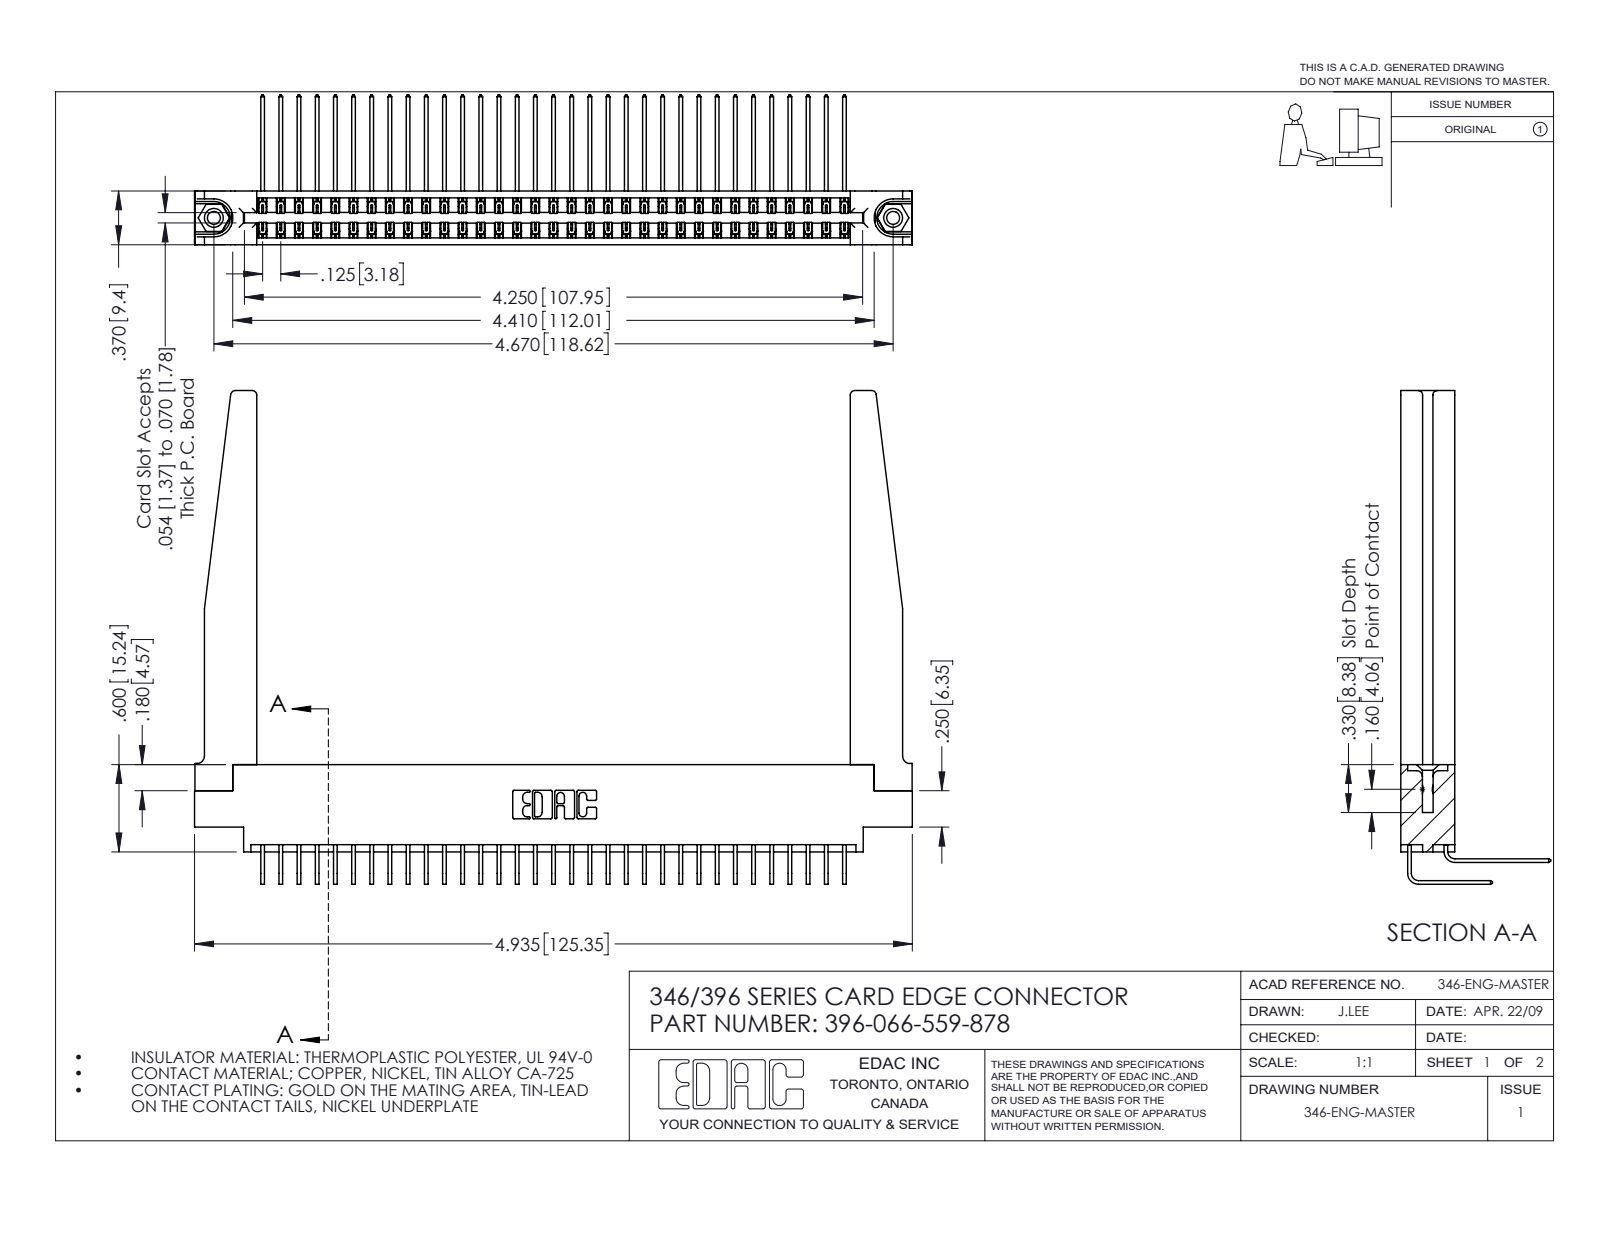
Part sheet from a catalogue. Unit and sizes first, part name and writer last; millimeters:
Units: millimetres
Overall size (bounding box): 125.3 × 86.2 × 26.2
Round holes (diameter × count): ⌀2.3 ×2, ⌀3.2 ×2, ⌀4 ×2, ⌀1.6 ×1
Round bosses / shafts (diameter × count): ⌀3.9 ×2
Partial cylindrical surfaces — rounded edges, fillets, slot ends (radius × count): R0.2 ×99, R0.3 ×22, R0.8 ×8, R0.2 ×6, R0.8 ×6, R1.3 ×4, R0.7 ×3, R0.4 ×2
Main face-to-face distances: 9.4, 1.2, 8.2, 1.8, 0.6, 3.8, 3.8, 6.4, 7.6, 7
Hole centre spacings: 6.2, 113.3, 118.6
Volume: 19 290 mm³ · Surface area: 25 420 mm²
Bodies: 71 solids, 3924 faces (2664 planar, 1208 cylindrical, 52 other)
Part name (STEP PRODUCT): 396-066-559-878; 345-292-001_558 559 Tail - 1; 346 Part_0.170 Offset - 0.156 Dia-TH; 346-220-078_345-220-078 (+2 more)
STEP written by: SolidWorks 2016 (CONFIG_CONTROL_DESIGN)
